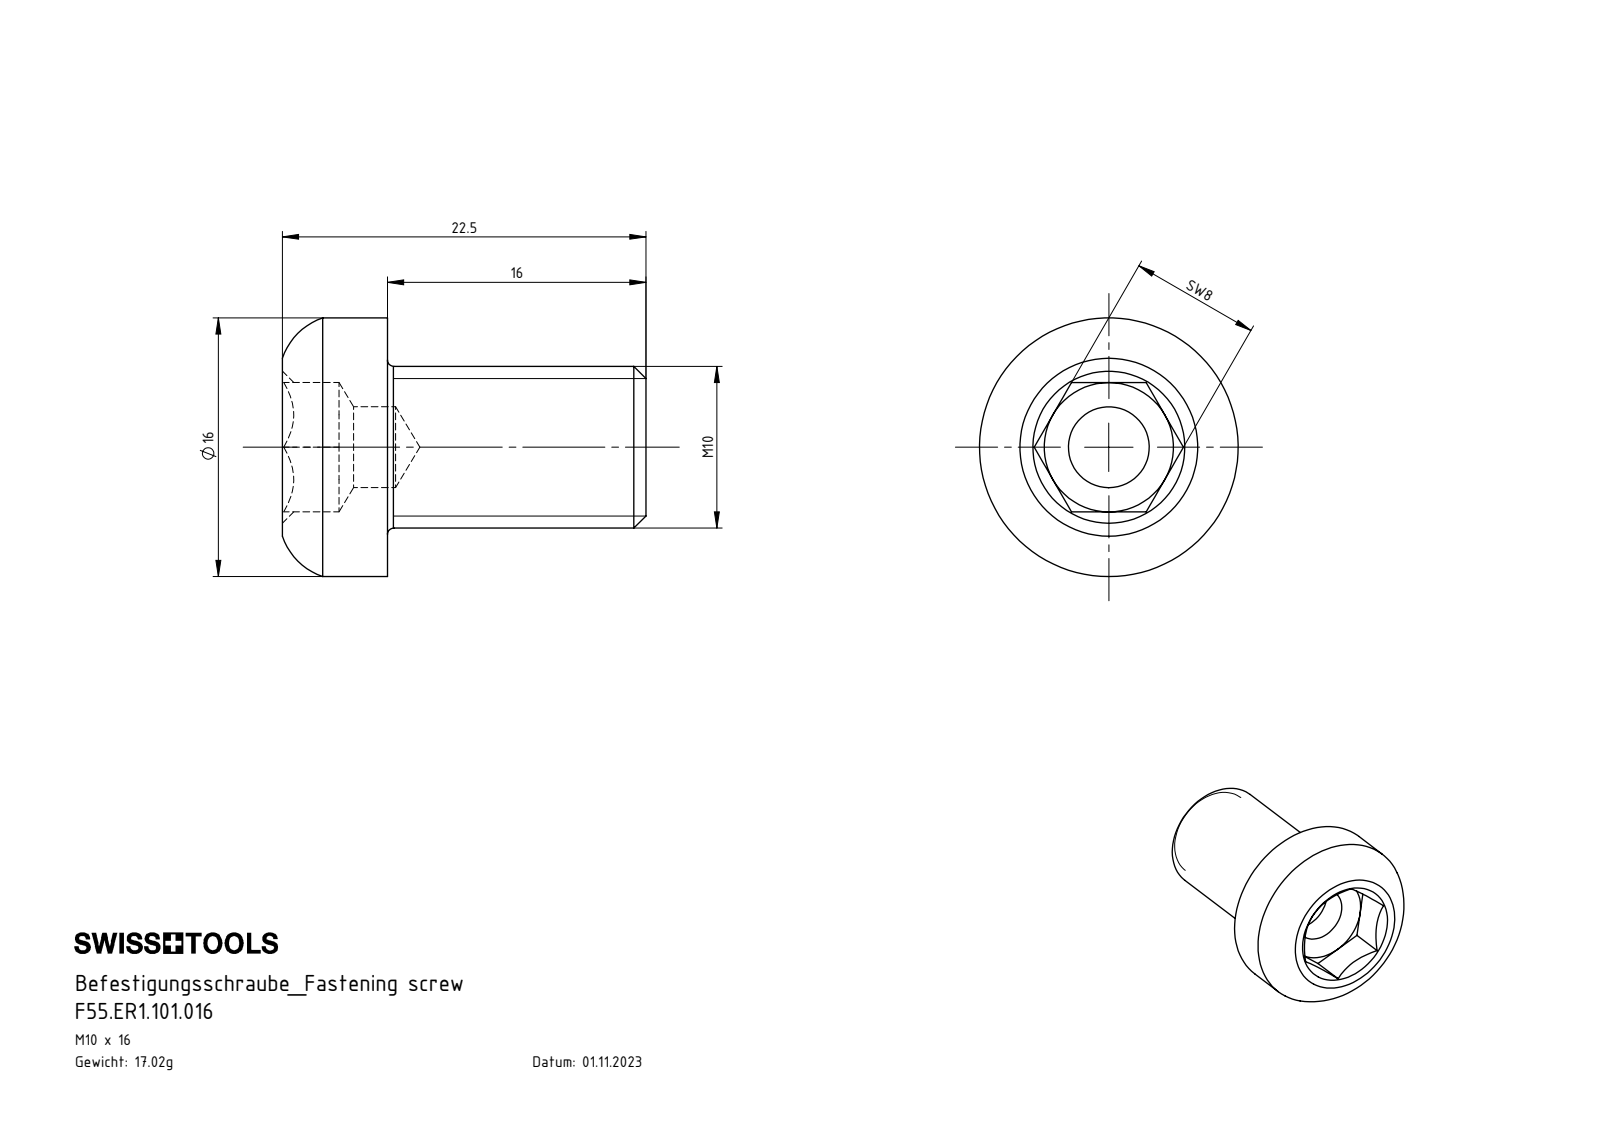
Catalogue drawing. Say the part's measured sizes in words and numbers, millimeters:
The part is named "F55.ER1.101.016". Its 3-D file was written by "SolidWorks 2017 (AUTOMOTIVE_DESIGN)". It is 1 solid with 33 faces: 15 planar, 6 cylindrical and 12 other. Overall it measures 22.5 by 16 by 16 millimeters. Its volume is 2 169 cubic millimeters and its surface area 1 278 square millimeters. Round holes: 1 of diameter 5. Round bosses or shafts: 1 of diameter 16, 1 of diameter 10. The main face-to-face distances are 16, 8, 6.5, 22.5, 3.5, 3, 19.
